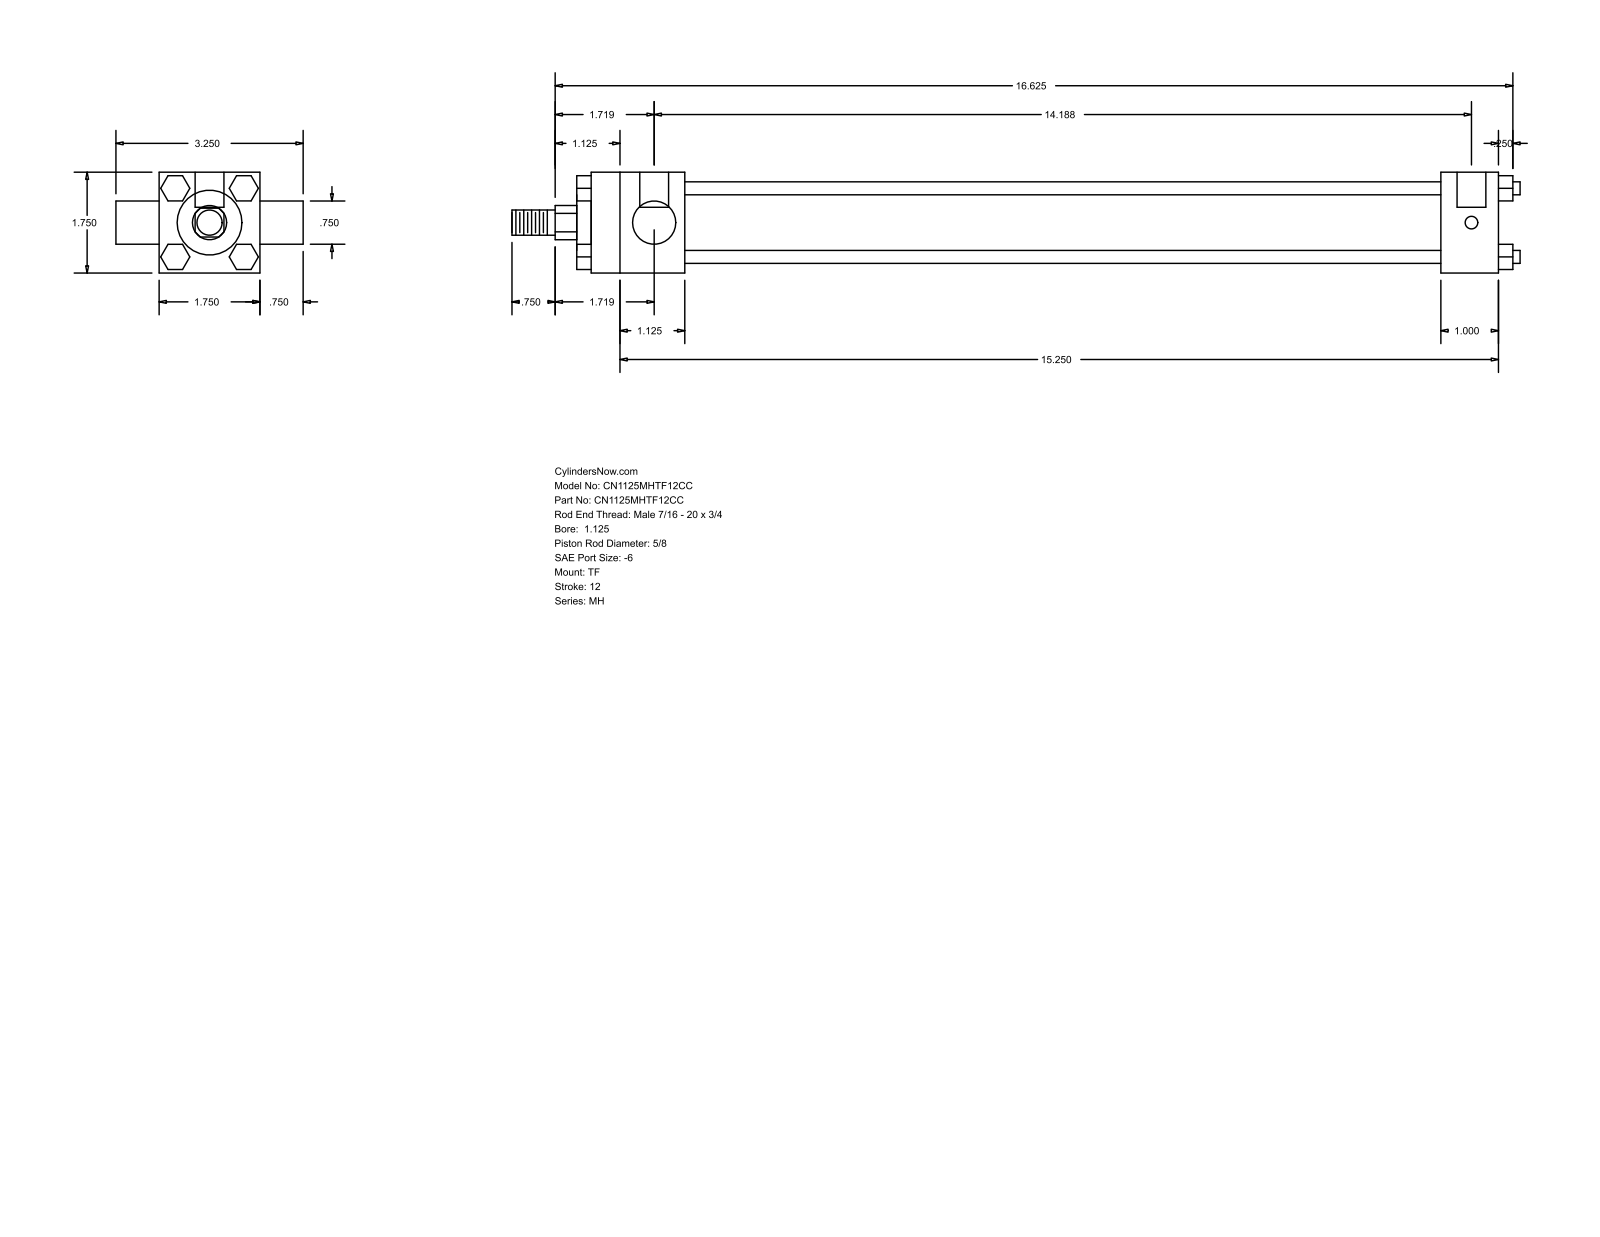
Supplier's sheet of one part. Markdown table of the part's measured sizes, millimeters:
| quantity | value |
| --- | --- |
| part name | MH_TF__0112_0.625 |
| STEP written by | GSSL Pune (CONFIG_CONTROL_DESIGN) |
| units | millimeters |
| bodies | 0 solids, 120 faces (92 planar, 28 cylindrical, 0 other) |
| overall size | 444.5 × 82.55 × 44.45 |
| round holes (diameter × count) | 5.56 × 3, 12.7 × 2 |
| round bosses / shafts (diameter × count) | 5.71 × 4, 34.92 × 1, 28.57 × 1, 19.05 × 1, 15.88 × 1, 11.11 × 1 |
| partial cylindrical surfaces (radius × count) | 7.54 × 1 |
| main face-to-face distances | 44.46, 11.11, 333.37, 358.78, 25.41, 41.27, 374.64, 400.05, 47.62, 6.35 |
| hole center spacings | 3.17, 357.19, 360.36 |
